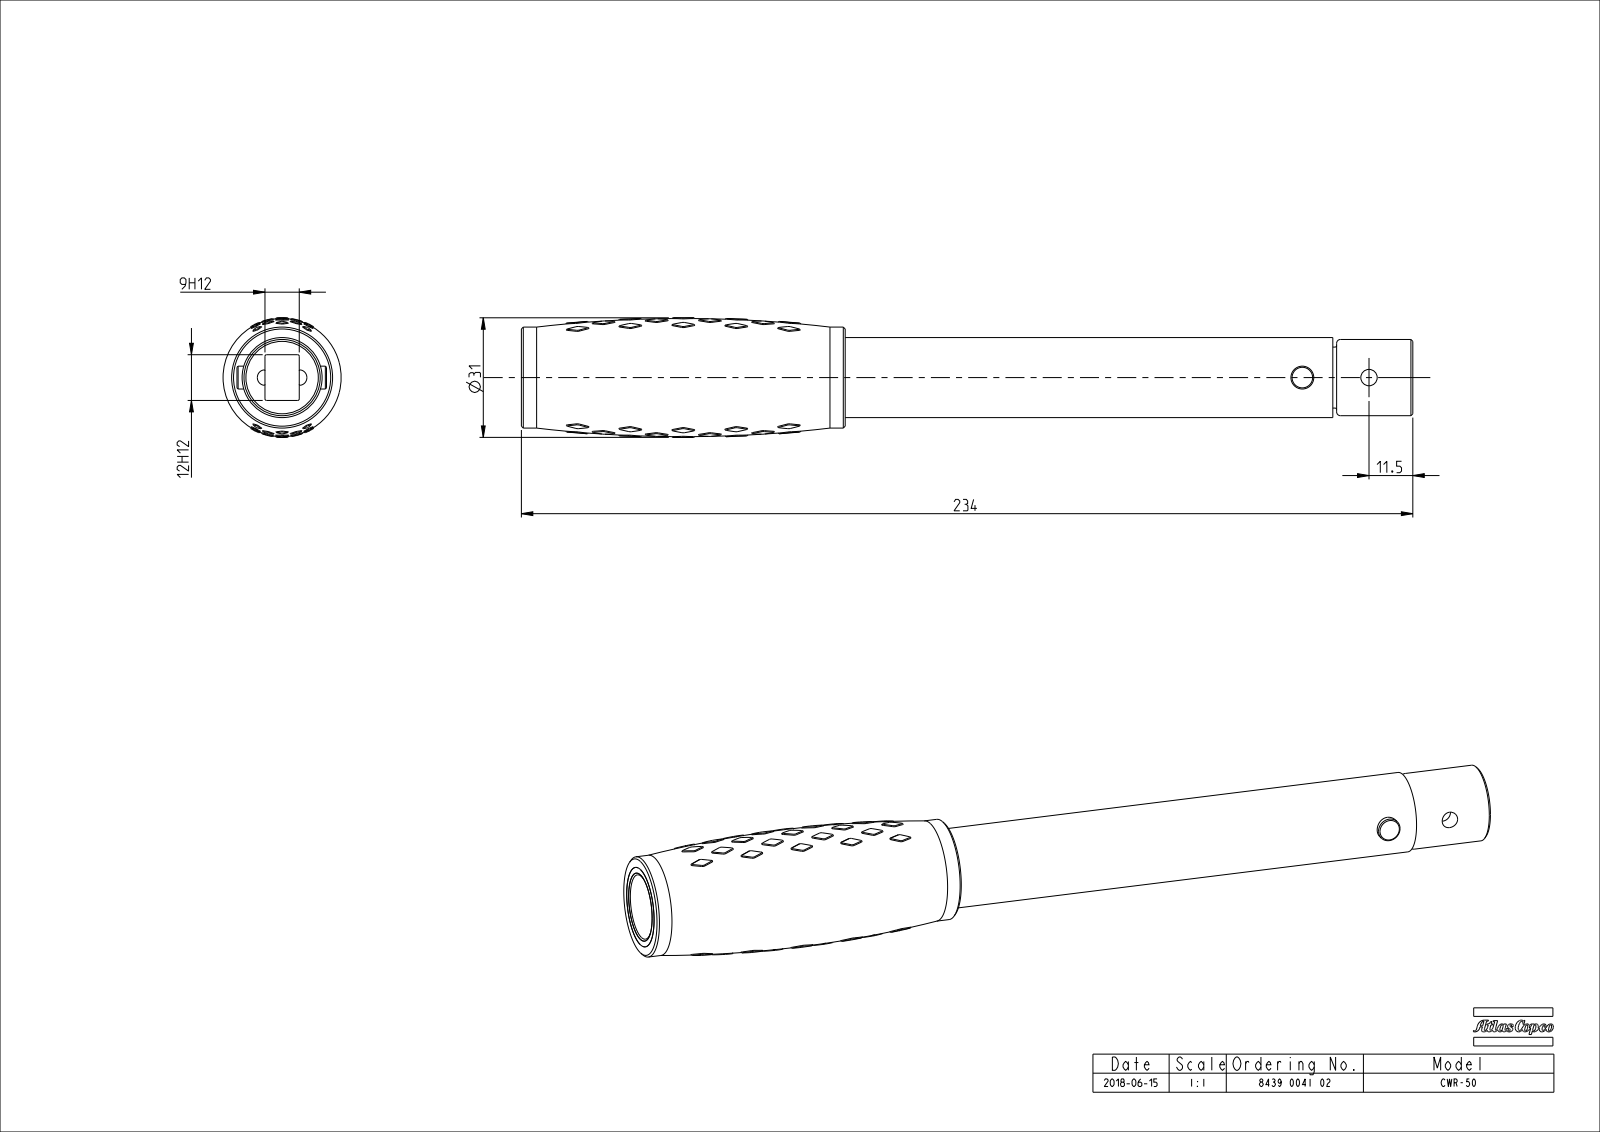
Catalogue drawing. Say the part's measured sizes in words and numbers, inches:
The part is named "8439004102". Its 3-D file was written by "SolidWorks 2016 (AUTOMOTIVE_DESIGN)". It is 0 solids with 411 faces: 14 planar, 36 cylindrical and 361 other. Overall it measures 9.213 by 1.237 by 1.22 inches. Round holes: 1 of diameter 0.169, 1 of diameter 0.65, 1 of diameter 0.827, 1 of diameter 1.043. Round bosses or shafts: 1 of diameter 0.787, 1 of diameter 0.63, 1 of diameter 0.236. Partial cylindrical surfaces (rounded edges, fillets, slot ends): 4 of radius 0.016, 4 of radius 0.079, 2 of radius 0.098. The main face-to-face distances are 3.346, 0.354, 0.472, 5.039, 8.386, 0.827, 5.866, 9.213, 0.285, 0.64.
